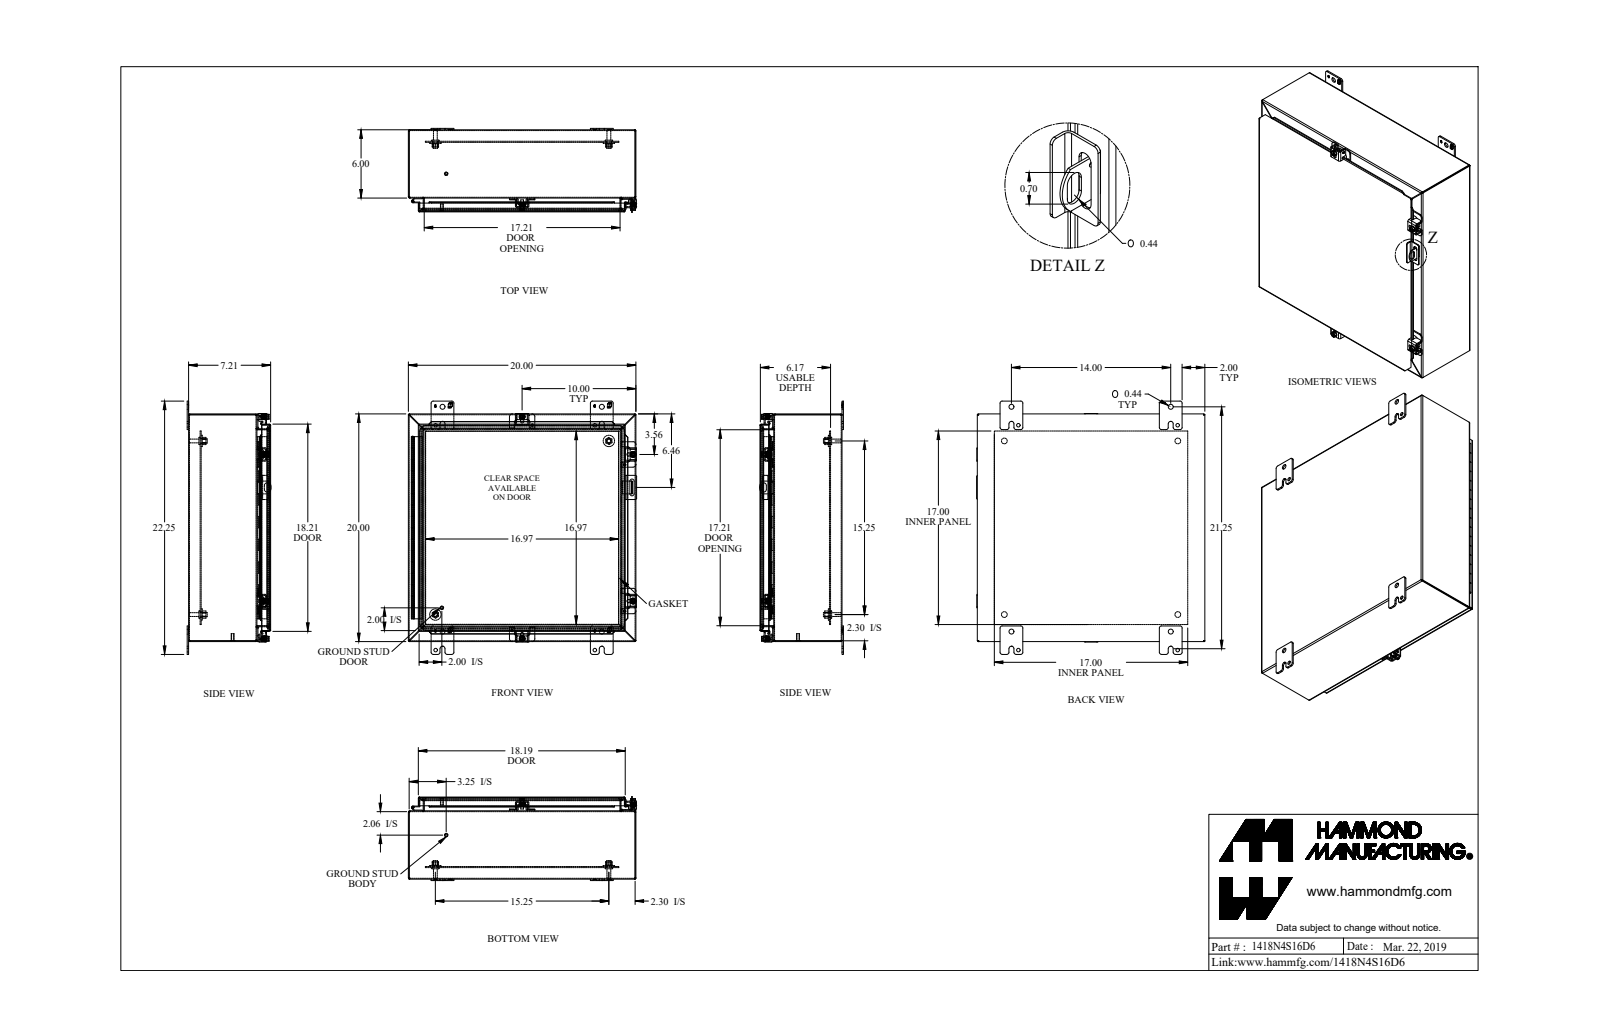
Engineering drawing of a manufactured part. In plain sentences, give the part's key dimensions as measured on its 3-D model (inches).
The part is named "1418N4S16D6_Default". Its 3-D file was written by "SolidWorks 2019 (CONFIG_CONTROL_DESIGN)". It is 39 solids with 1329 faces: 728 planar, 467 cylindrical and 134 other. Overall it measures 22.25 by 20.063 by 7.375 inches. Its volume is 145.1 cubic inches and its surface area 3 827 square inches. Round holes: 4 of diameter 0.213, 4 of diameter 0.265, 4 of diameter 0.313, 4 of diameter 0.375, 4 of diameter 0.437, 4 of diameter 0.5, 2 of diameter 0.307, 2 of diameter 0.445, 1 of diameter 0.11, 1 of diameter 0.125. Round bosses or shafts: 4 of diameter 0.65, 4 of diameter 0.5, 4 of diameter 0.39, 4 of diameter 0.375, 4 of diameter 0.332, 4 of diameter 0.244, 2 of diameter 1, 2 of diameter 0.313. Partial cylindrical surfaces (rounded edges, fillets, slot ends): 26 of radius 0.188, 24 of radius 0.036, 24 of radius 0.108, 21 of radius 0.048, 21 of radius 0.143, 20 of radius 0.25, 10 of radius 0.125, 8 of radius 0.045. The main face-to-face distances are 0.072, 19.928, 7.066, 7.138, 7.138, 0.072, 7.21, 0.937, 1.009, 0.095. The hole center spacings are 15.25, 7.916, 14, 18.975, 22.237, 2.434, 3.065, 16.762.
